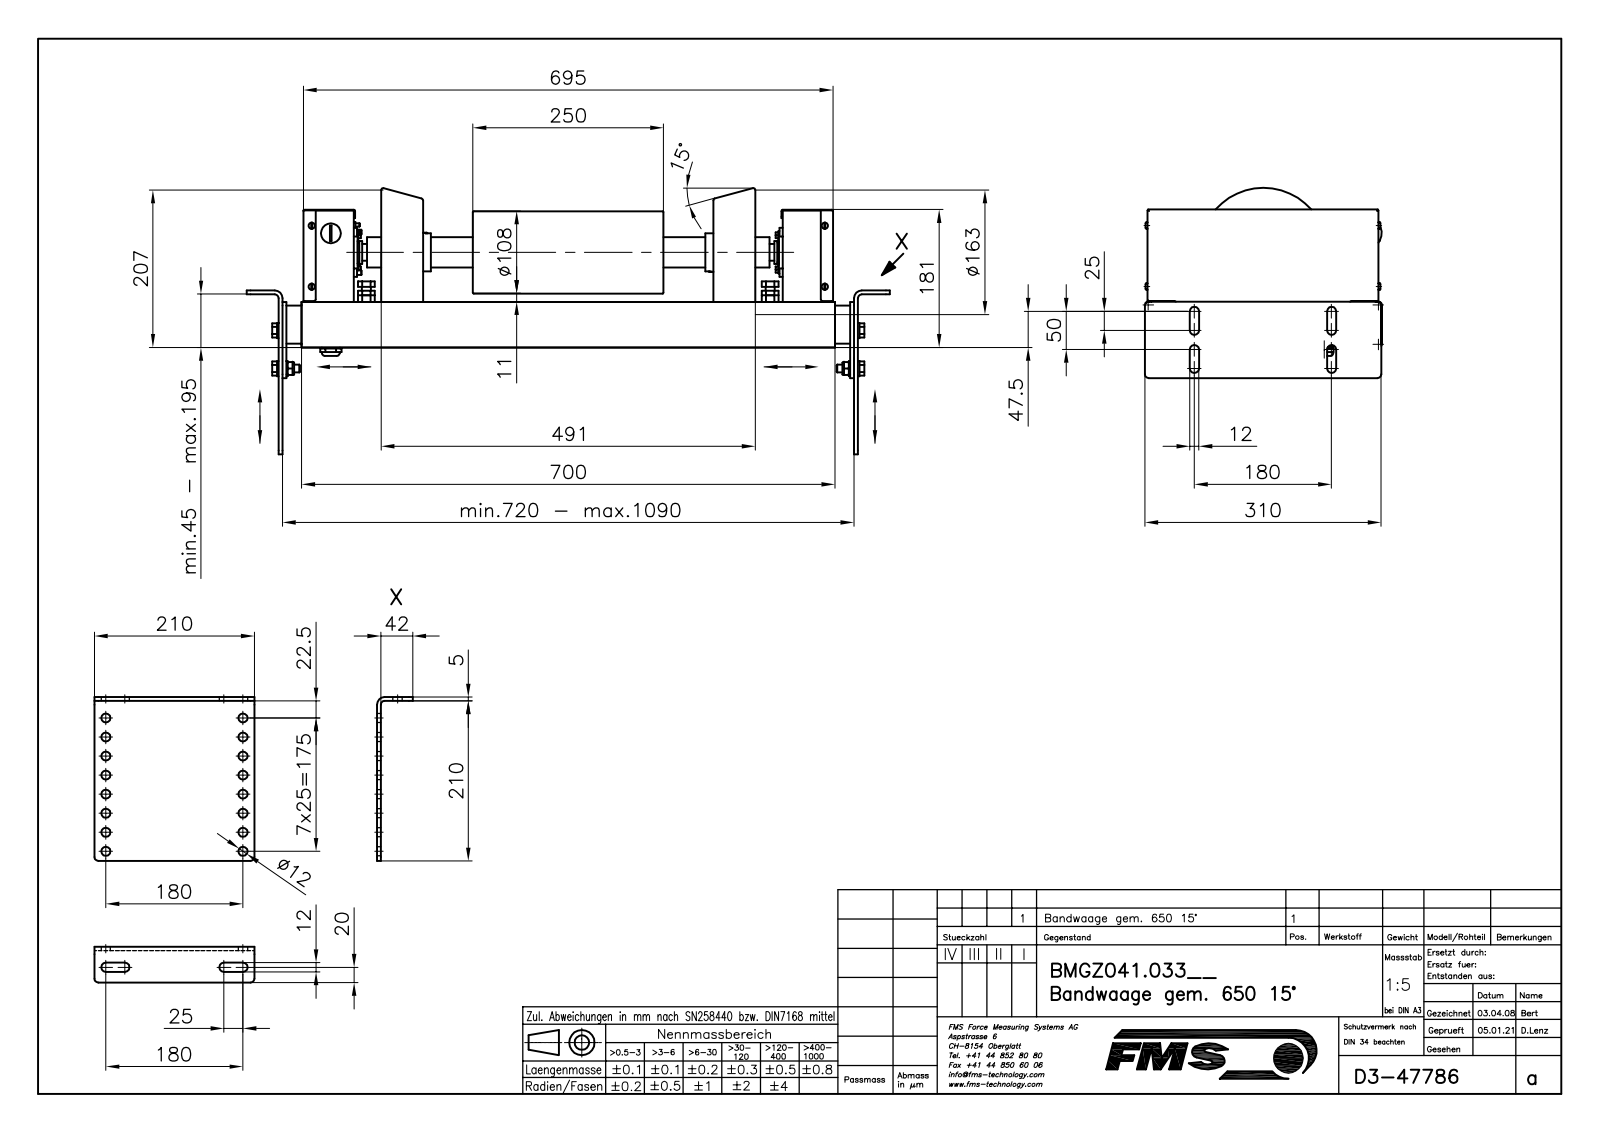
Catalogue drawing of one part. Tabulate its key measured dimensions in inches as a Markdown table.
| quantity | value |
| --- | --- |
| part name | B47786_STP; B50029; B46957; B4695602 (+8 more) |
| STEP written by | Mechanical Desktop 2009 (CONFIG_CONTROL_DESIGN) |
| units | inches |
| bodies | 161 solids, 2676 faces (1371 planar, 962 cylindrical, 343 other) |
| overall size | 33.228 × 13.75 × 12.232 |
| volume | 442.1 in³ |
| surface area | 4 822 in² |
| round holes (diameter × count) | 0.472 × 17, 0.197 × 6, 0.138 × 4, 0.193 × 4, 0.252 × 4, 0.342 × 4, 0.344 × 4, 0.394 × 4, 0.413 × 4, 0.42 × 4, 0.583 × 4, 0.161 × 3 |
| round bosses / shafts (diameter × count) | 0.472 × 11, 0.323 × 8, 0.165 × 8, 0.787 × 6, 0.394 × 6, 0.197 × 5, 0.63 × 4, 0.437 × 4 |
| partial cylindrical surfaces (radius × count) | 0.079 × 34, 0.039 × 24, 0.157 × 16, 0.197 × 16, 0.236 × 14, 0.138 × 8, 0.089 × 6, 0.02 × 4 |
| main face-to-face distances | 0.157, 0.197, 0.039, 10.63, 1.417, 10.472, 1.26, 2.205, 10.787, 1.575 |
| hole center spacings | 0.984, 7.155, 1.969, 7.355, 2.953, 7.677, 3.937, 7.087 |
